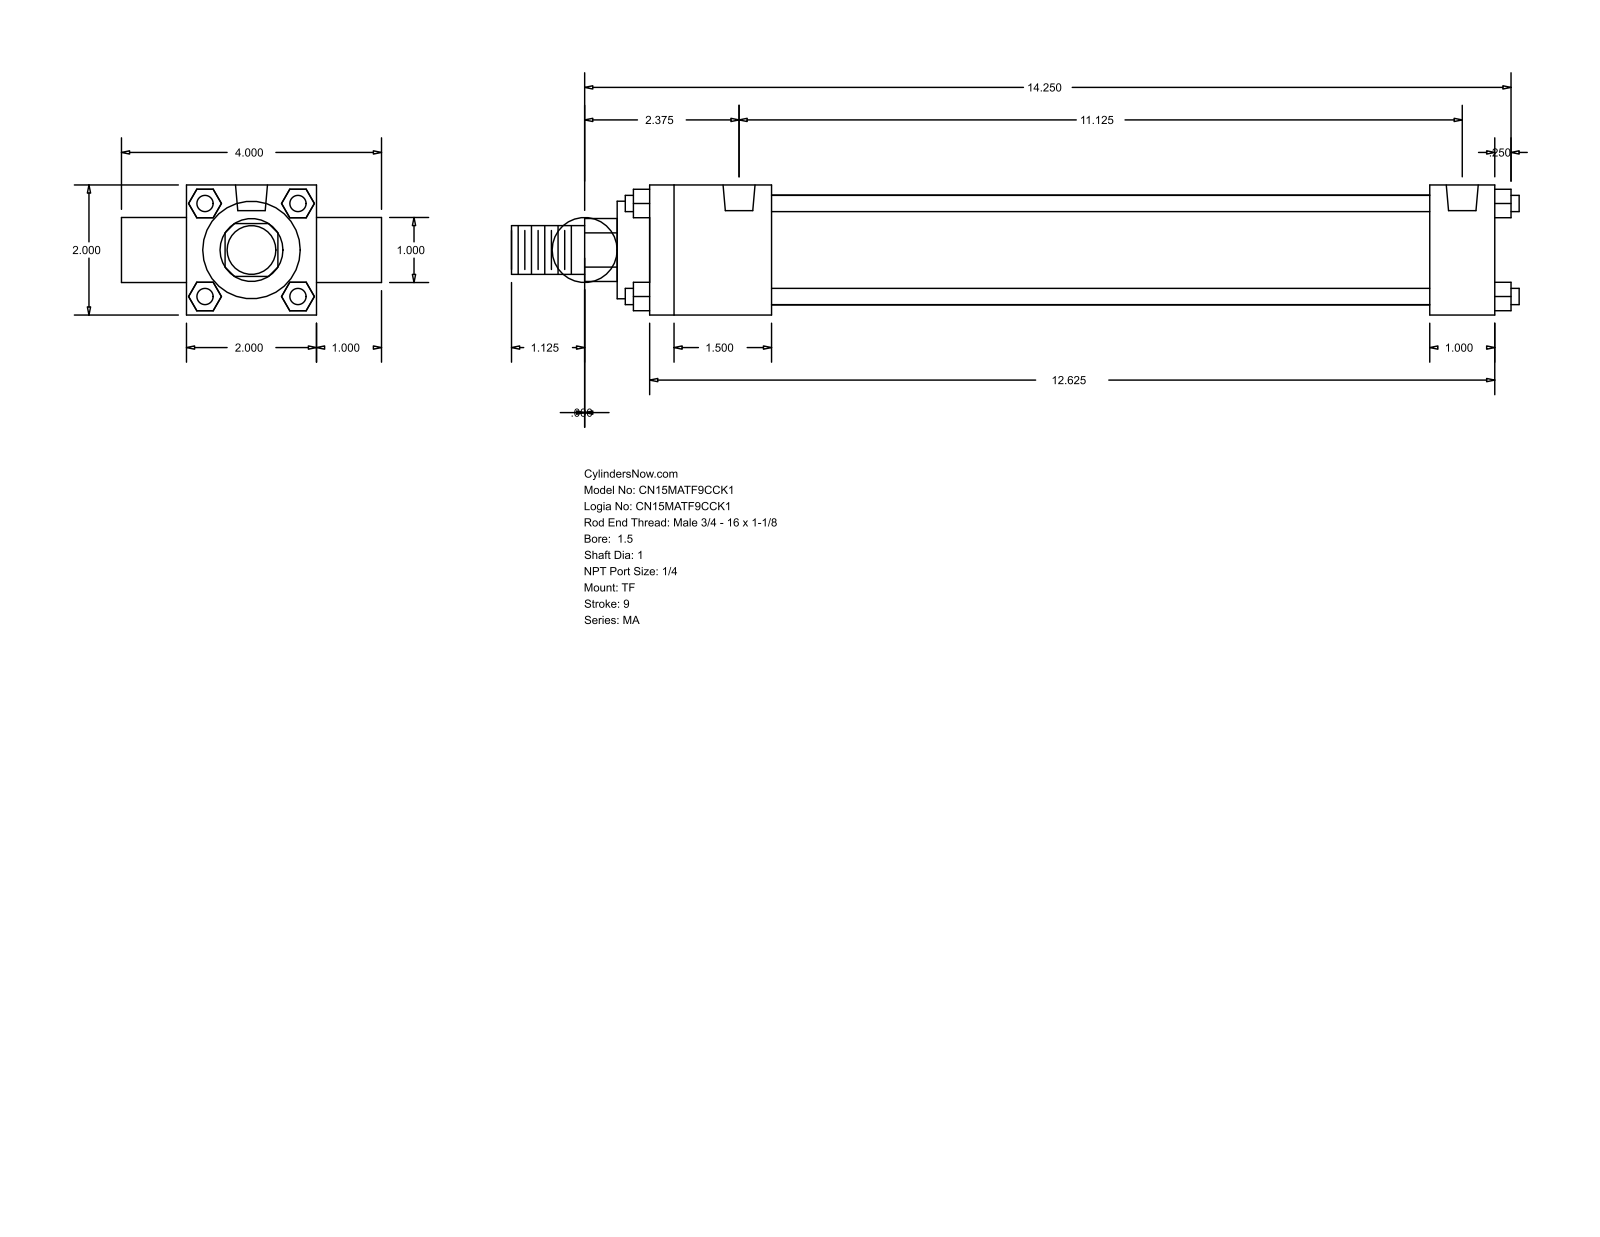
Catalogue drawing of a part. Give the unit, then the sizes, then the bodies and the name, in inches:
Units: inches
Overall size (bounding box): 15.5 × 4 × 2
Round holes (diameter × count): ⌀0.313 ×3, ⌀0.492 ×2
Round bosses / shafts (diameter × count): ⌀0.25 ×4, ⌀1 ×2, ⌀1.69 ×1, ⌀1.5 ×1, ⌀0.75 ×1
Partial cylindrical surfaces — rounded edges, fillets, slot ends (radius × count): R0.484 ×1
Main face-to-face distances: 2, 1, 13, 3, 0.25, 1.875, 12, 10.125, 11.125, 13.5
Hole centre spacings: 11.125
Bodies: 0 solids, 120 faces (92 planar, 28 cylindrical, 0 other)
Part name (STEP PRODUCT): MA_TF__0150_1
STEP written by: GSSL Pune (CONFIG_CONTROL_DESIGN)
